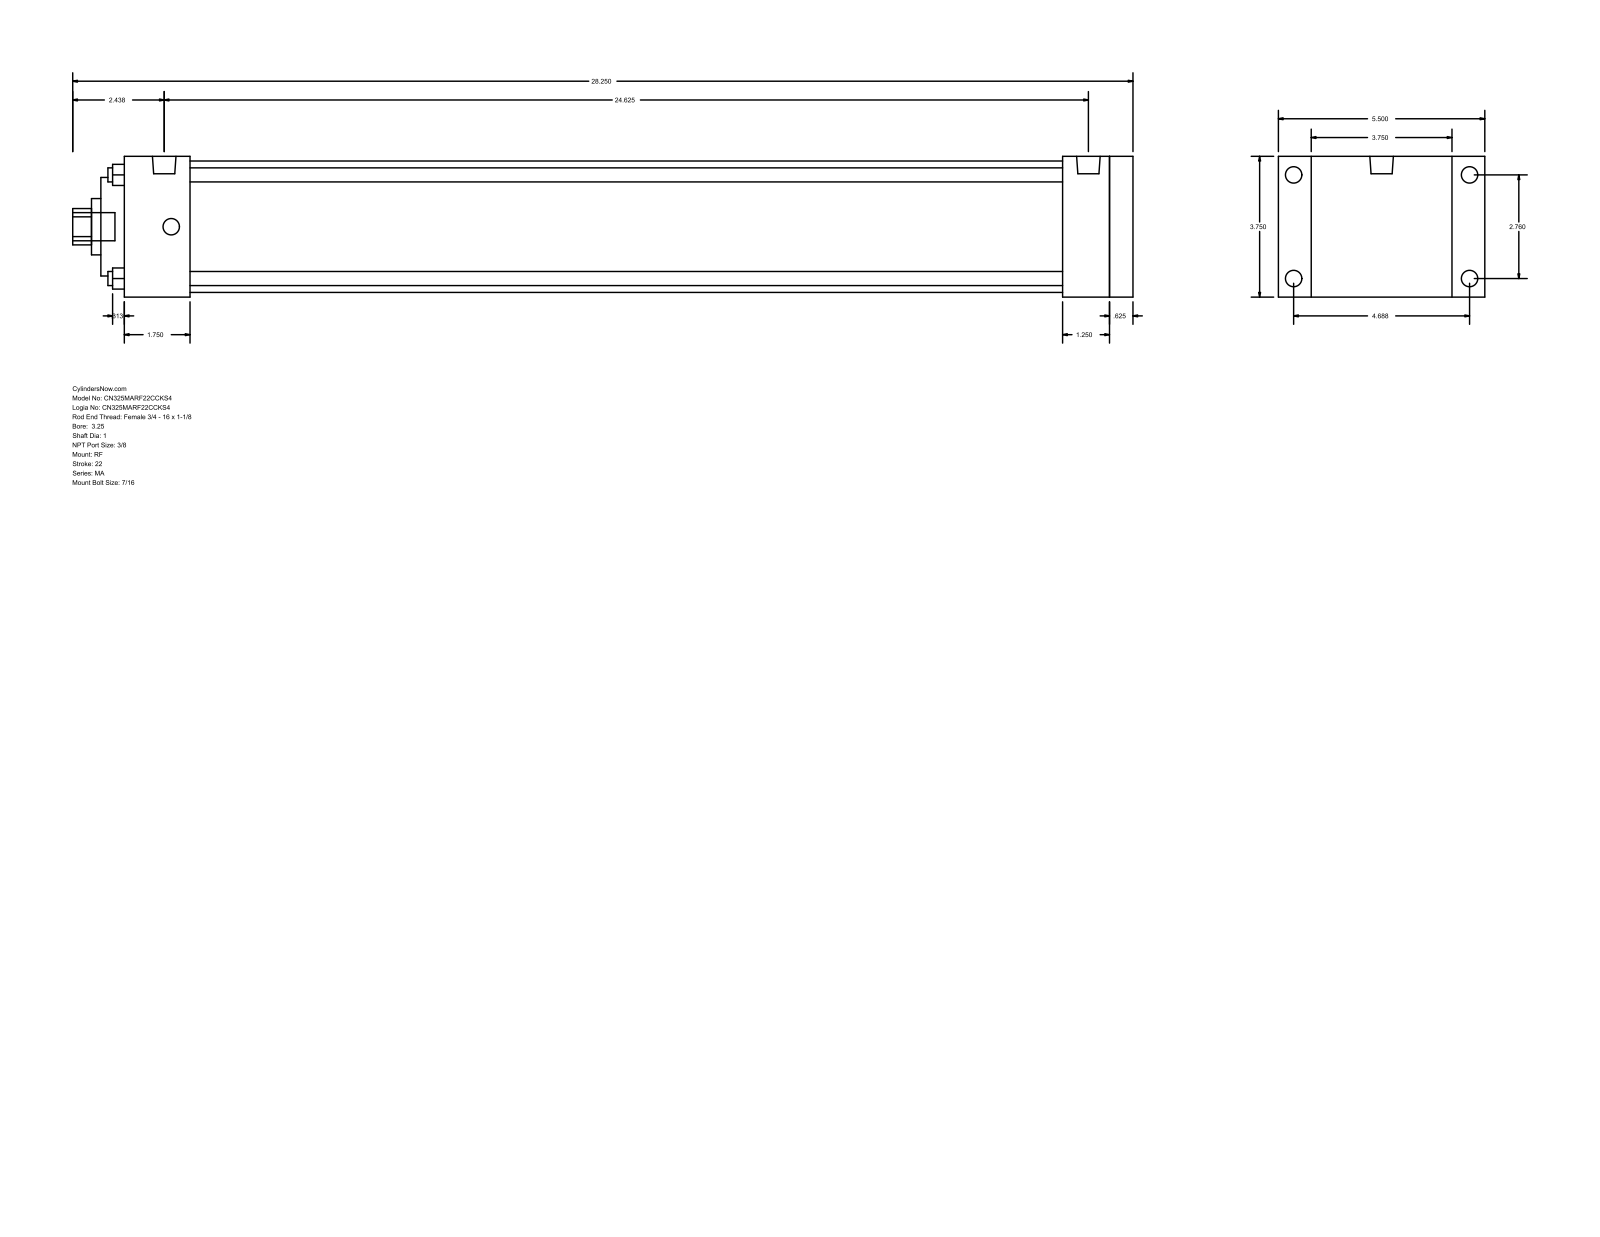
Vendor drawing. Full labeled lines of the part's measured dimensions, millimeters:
Part name (STEP PRODUCT): MA_RF__0325_1
STEP written by: GSSL Pune (CONFIG_CONTROL_DESIGN)
Units: millimetres
Bodies: 0 solids, 94 faces (65 planar, 29 cylindrical, 0 other)
Overall size (bounding box): 717.55 × 139.7 × 95.25
Round holes (diameter × count): ⌀9.53 ×4, ⌀25.4 ×1, ⌀38.1 ×1, ⌀66.67 ×1, ⌀88.9 ×1
Round bosses / shafts (diameter × count): ⌀11.11 ×8, ⌀15.93 ×2, ⌀19.05 ×1
Partial cylindrical surfaces — rounded edges, fillets, slot ends (radius × count): R12.29 ×1
Main face-to-face distances: 95.24, 682.63, 666.75, 15.88, 22.23, 117.47, 15.87, 635, 31.75, 47.63
Hole centre spacings: 49.57, 70.1, 99.14
